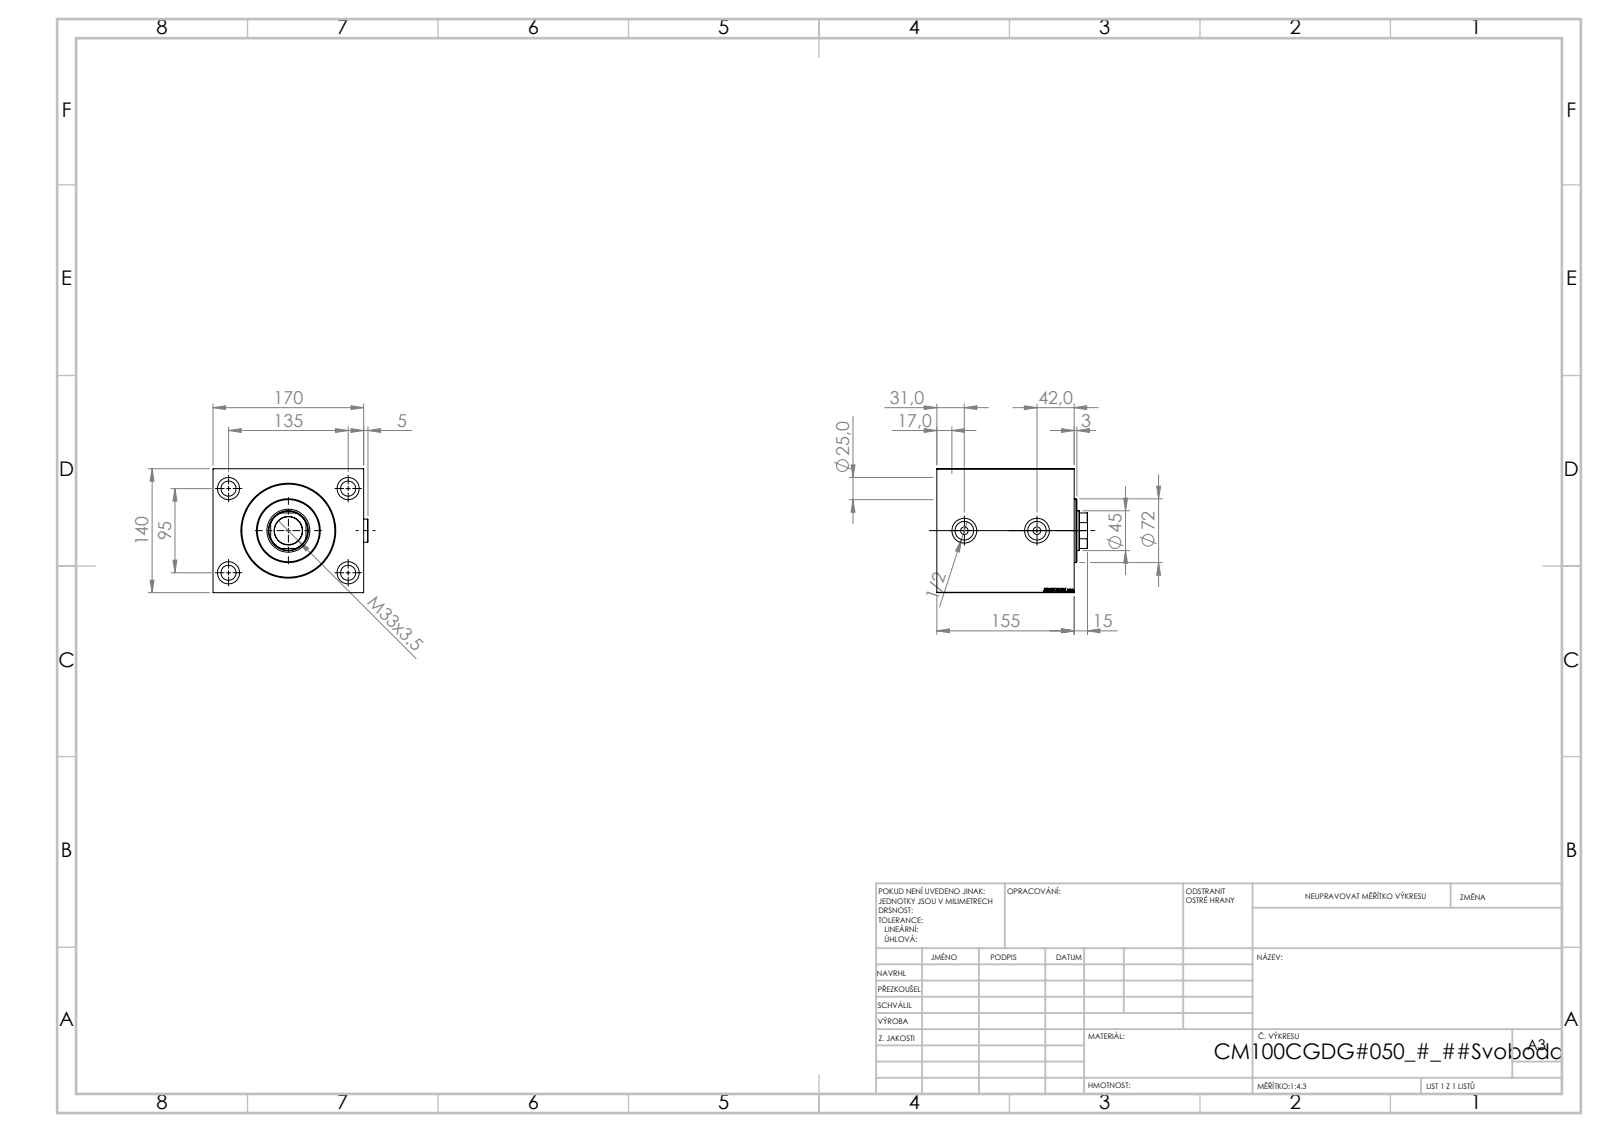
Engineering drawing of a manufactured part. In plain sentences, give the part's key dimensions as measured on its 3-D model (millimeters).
The part is named "V450CM_C_VCP; V450CM_VC_B; Zatka_OIL_PORT; V450CM_C_Body". Its 3-D file was written by "SolidWorks 2019 (CONFIG_CONTROL_DESIGN)". It is 5 solids with 919 faces: 443 planar, 78 cylindrical and 398 other. Overall it measures 174.9 by 170 by 140 millimeters. Its volume is 3 178 000 cubic millimeters and its surface area 300 264 square millimeters. Round holes: 4 of diameter 17, 4 of diameter 25, 2 of diameter 8.5, 2 of diameter 20.96, 2 of diameter 28, 1 of diameter 31.5, 1 of diameter 45, 1 of diameter 48.5, 1 of diameter 100, 1 of diameter 102, 1 of diameter 105. Round bosses or shafts: 2 of diameter 26, 1 of diameter 72. Partial cylindrical surfaces (rounded edges, fillets, slot ends): 1 of radius 22. The main face-to-face distances are 140, 170, 155, 129, 26, 15, 114, 65, 50, 90. The hole center spacings are 82.54, 95, 135, 165.08, 82.
